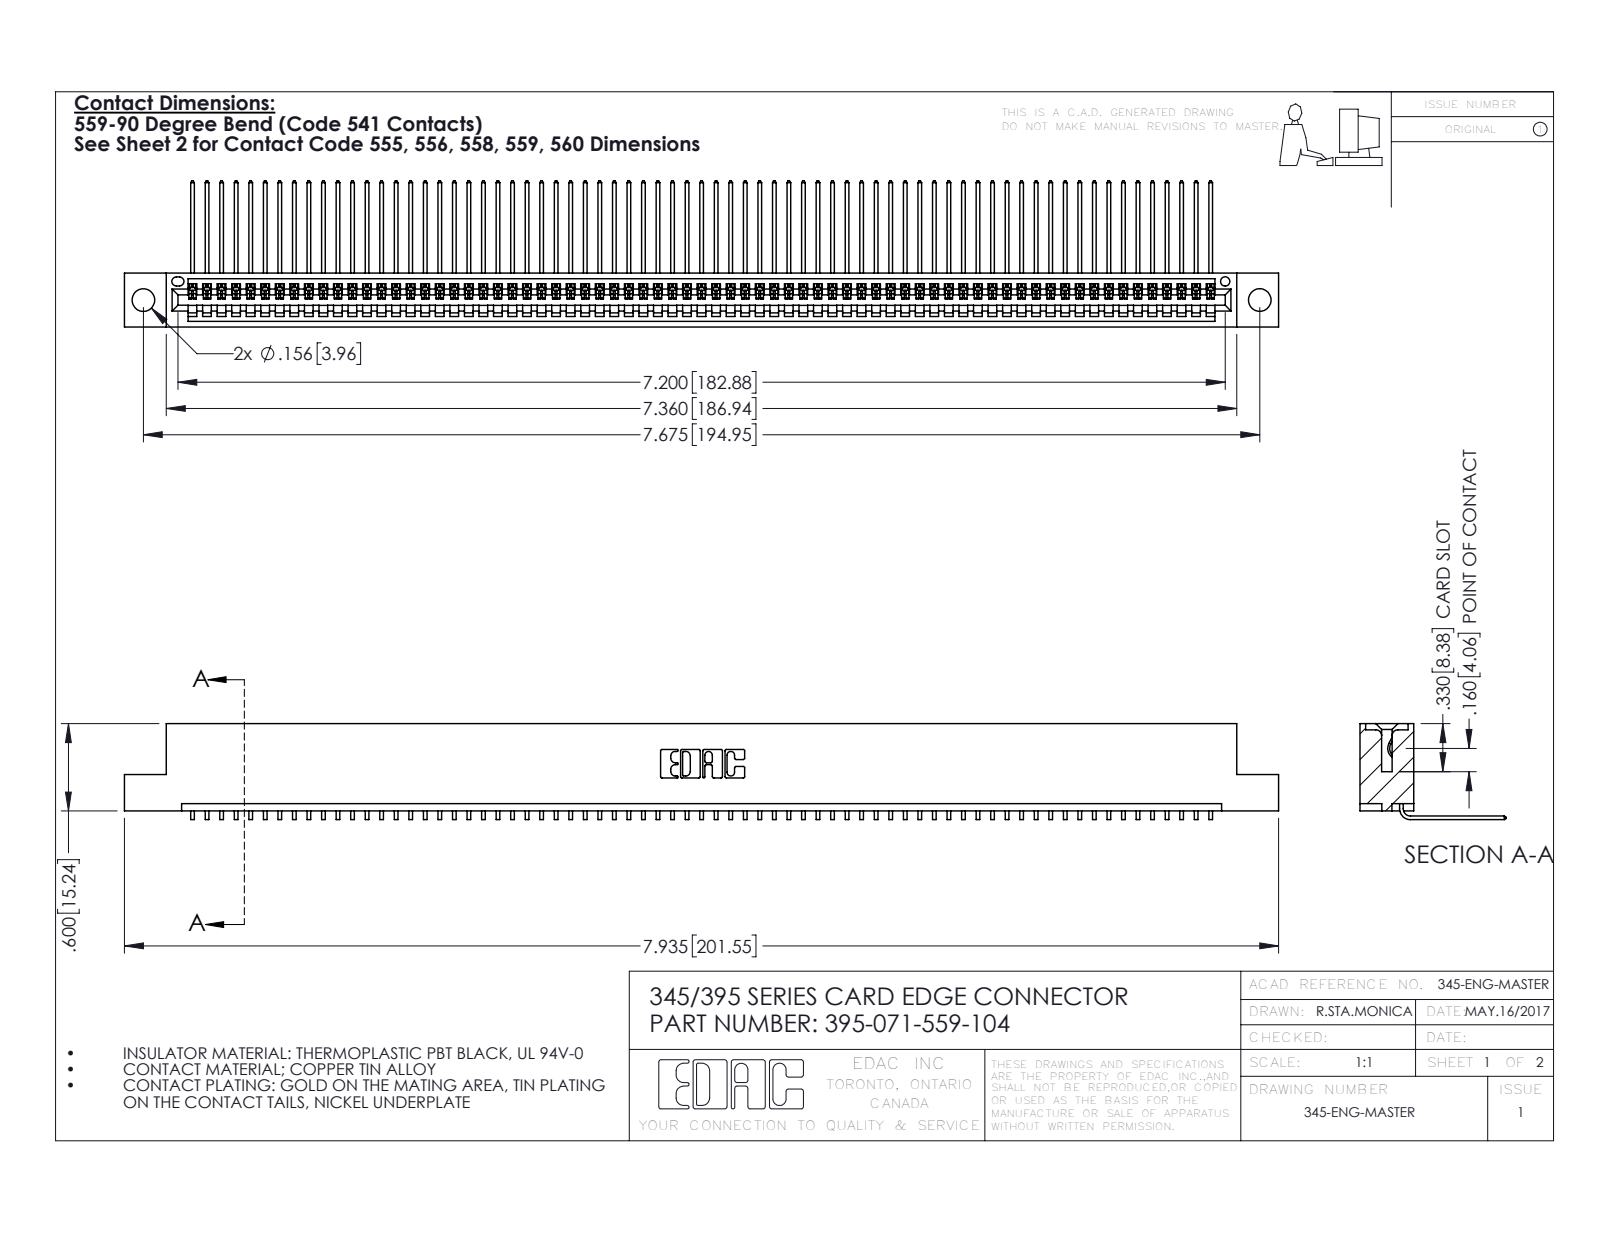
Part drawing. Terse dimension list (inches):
name: 345-292-001_558 559 Tail - 1; 395-071-559-104; 345 Part_Flush Mounting Lugs - 0.156 Dia-TH
written by: SolidWorks 2016 (CONFIG_CONTROL_DESIGN)
unit: in
bodies: 72 solids, 4386 faces (3062 planar, 1324 cylindrical, 0 other)
size: 7.935 × 1.005 × 0.659
volume: 1.192 in³; area: 42.7 in²
holes: 2× ⌀0.156, 1× ⌀0.064
rounds: 142× R0.006, 22× R0.01, 6× R0.007, 6× R0.031, 3× R0.026, 2× R0.031, 2× R0.04, 1× R0.014
face distances: 0.298, 0.072, 0.37, 0.2, 0.098, 0.272, 0.025, 0.225, 0.149, 0.072
hole spacings: 0.27, 7.439, 7.675
